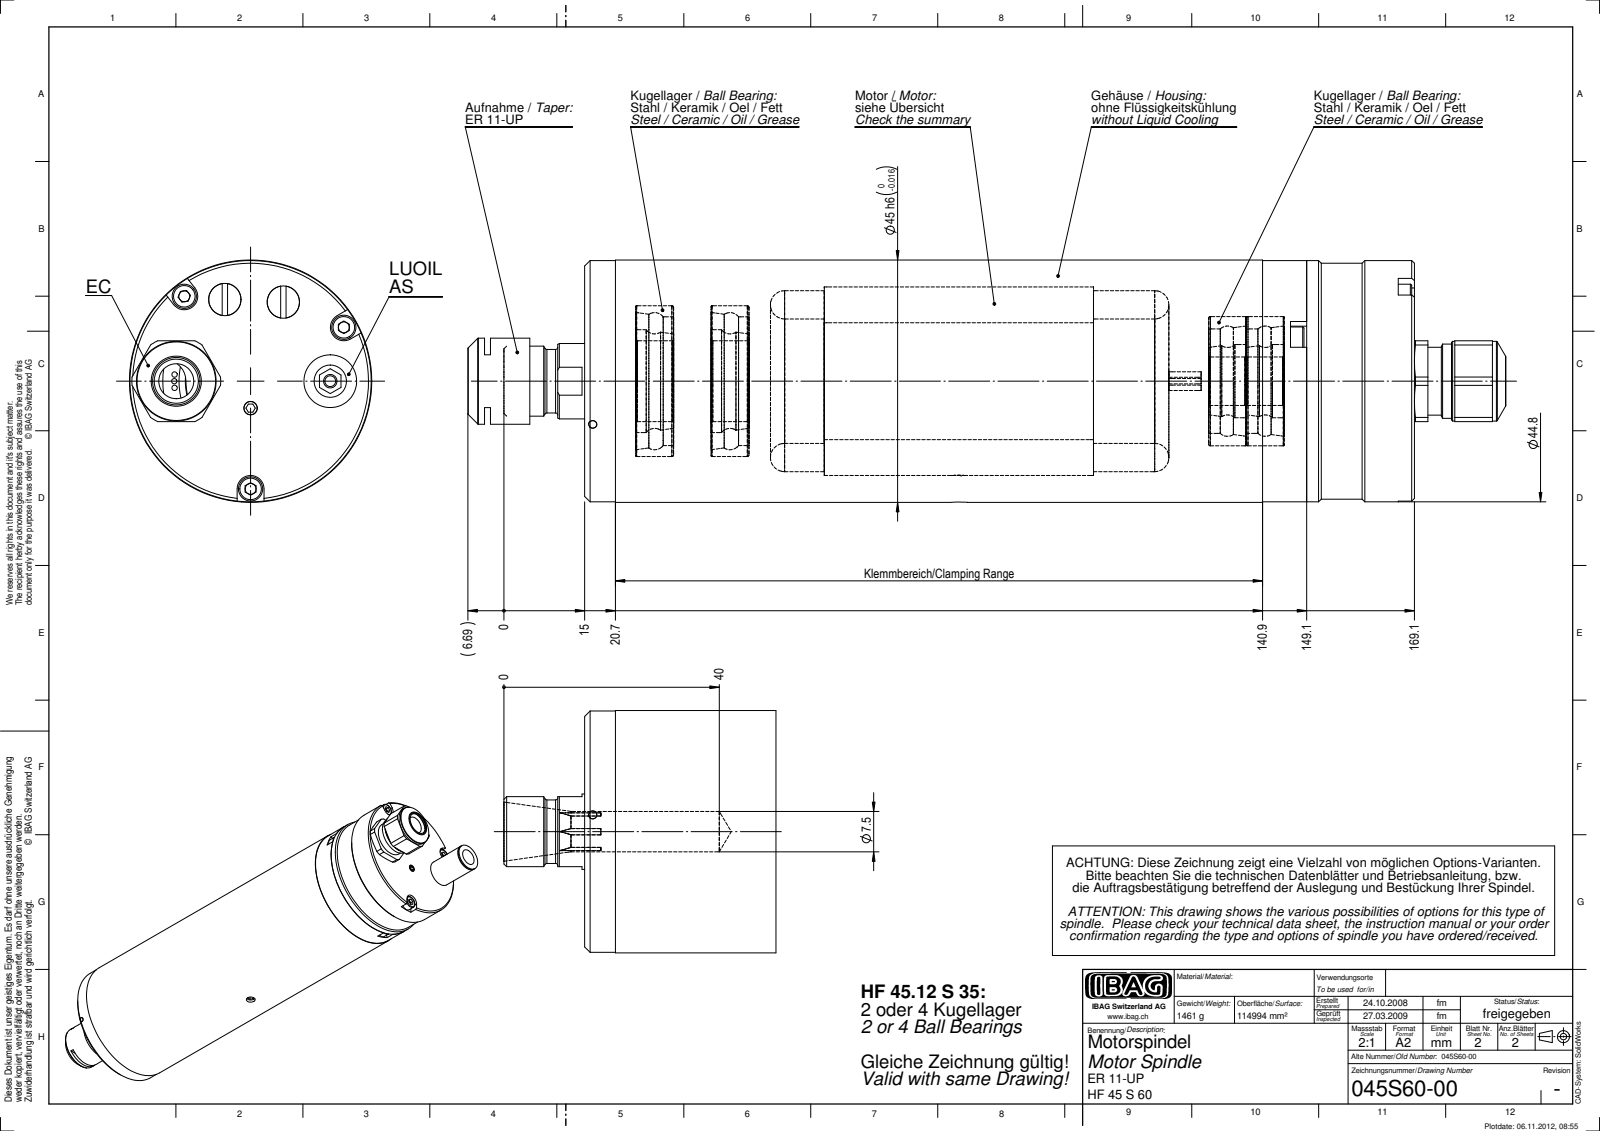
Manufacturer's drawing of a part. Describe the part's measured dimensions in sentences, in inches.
The part is named "045S60-00". Its 3-D file was written by "SolidWorks 2012 (CONFIG_CONTROL_DESIGN)". It is 0 solids with 342 faces: 160 planar, 108 cylindrical and 74 other. Overall it measures 7.59 by 1.772 by 1.772 inches. Round holes: 3 of diameter 0.217, 3 of diameter 0.236, 1 of diameter 0.079, 1 of diameter 0.13, 1 of diameter 0.256, 1 of diameter 0.323, 1 of diameter 0.567, 1 of diameter 0.591. Round bosses or shafts: 9 of diameter 0.177, 1 of diameter 1.772, 1 of diameter 1.764, 1 of diameter 1.724, 1 of diameter 0.63, 1 of diameter 0.583, 1 of diameter 0.551, 1 of diameter 0.543. Partial cylindrical surfaces (rounded edges, fillets, slot ends): 3 of radius 0.098, 3 of radius 0.102, 1 of radius 0.059, 1 of radius 0.063, 1 of radius 0.325. The main face-to-face distances are 0.787, 5.28, 6.067, 0.224, 5.055, 5.843, 4.957, 4.732, 0.323, 1.11. The hole center spacings are 0.717, 0.626, 0.172, 0.29, 0.331, 0.404, 0.428, 0.543.
